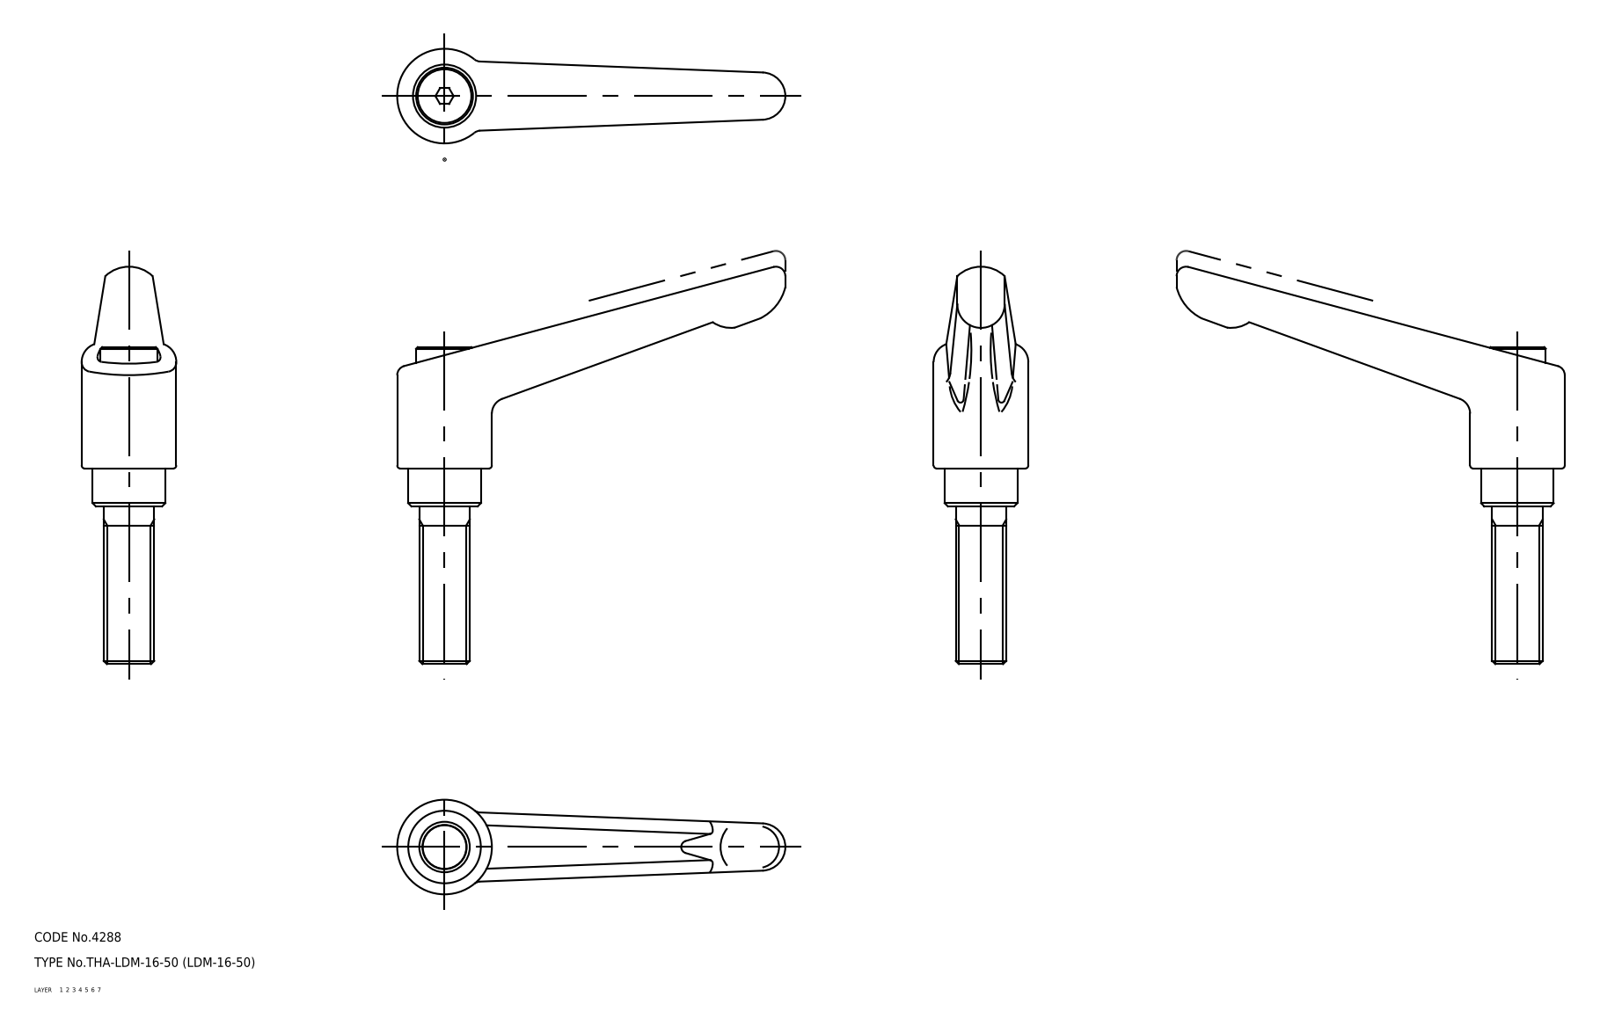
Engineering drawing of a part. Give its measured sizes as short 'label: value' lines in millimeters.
name: sleeve; screw; handle; LDM_16_50_12408_36
written by: CADfix (AUTOMOTIVE_DESIGN)
unit: mm
bodies: 3 solids, 92 faces (0 planar, 0 cylindrical, 92 other)
size: 126 × 123 × 30
volume: 55 548 mm³; area: 19 895 mm²
